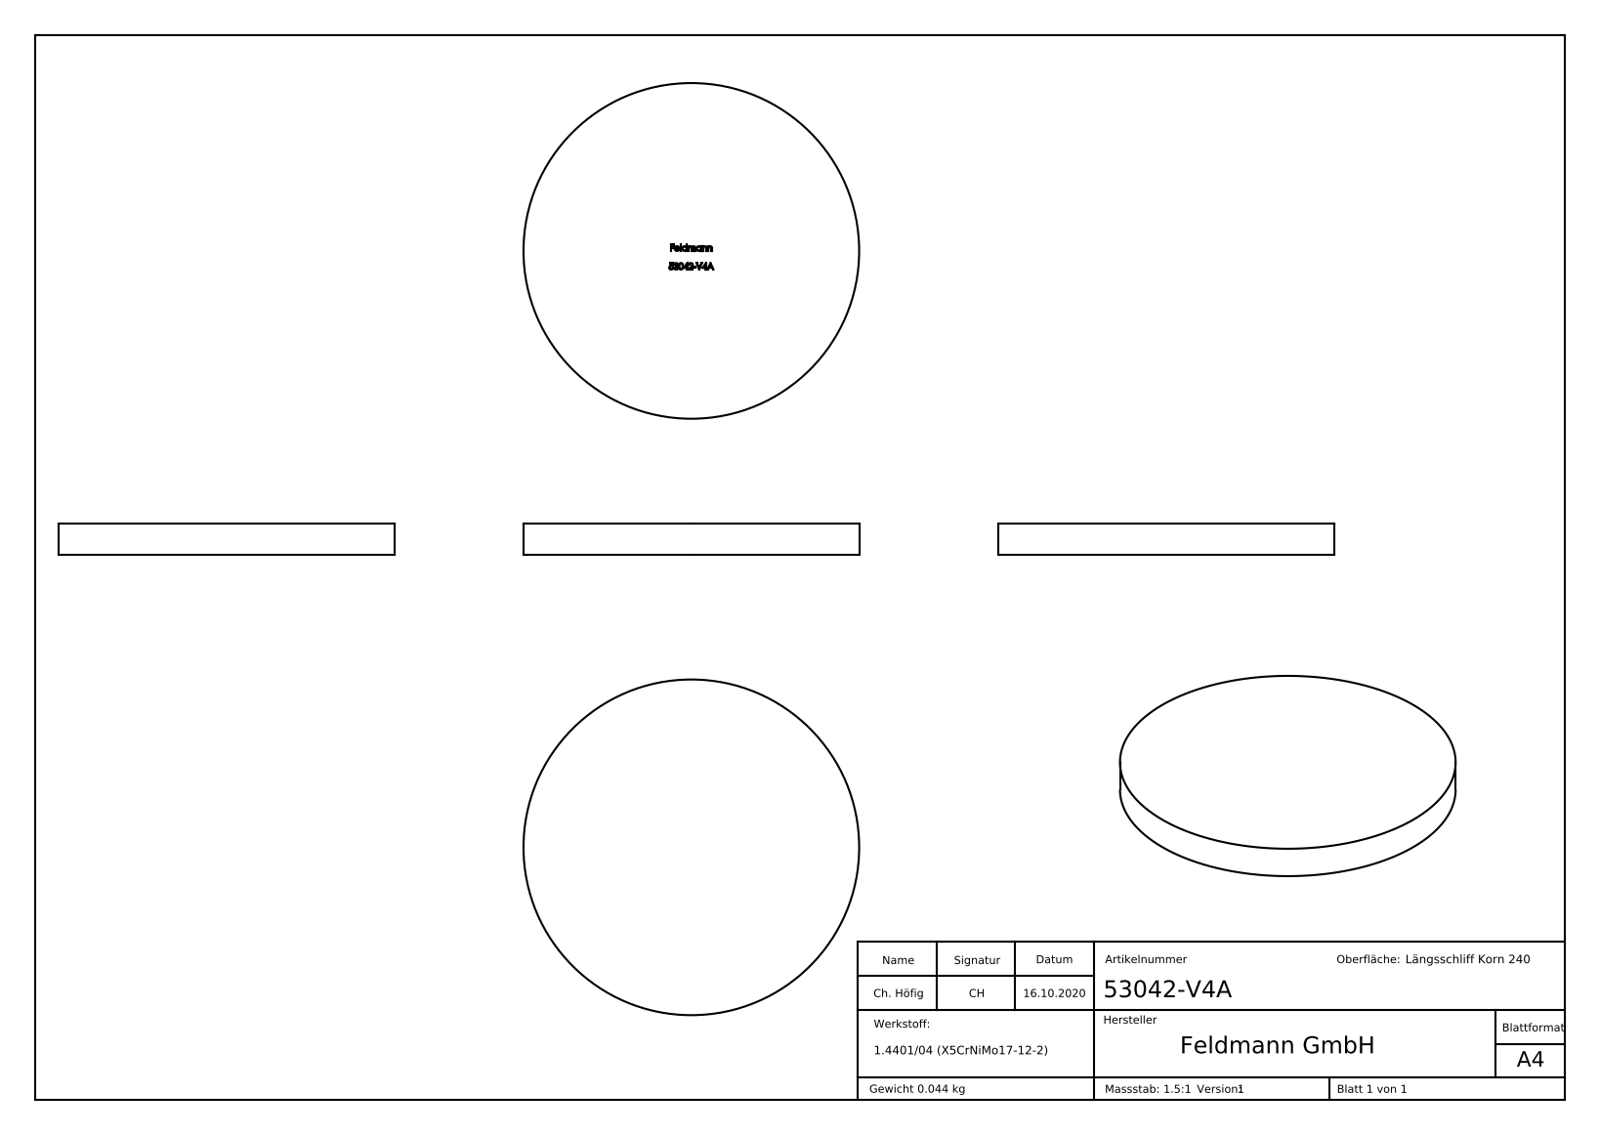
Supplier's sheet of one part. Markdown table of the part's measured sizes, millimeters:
| quantity | value |
| --- | --- |
| part name | 53042-V4A |
| STEP written by | SolidWorks 2018 (CONFIG_CONTROL_DESIGN) |
| units | millimeters |
| bodies | 1 solid, 230 faces (143 planar, 2 cylindrical, 85 other) |
| overall size | 42 × 42 × 4 |
| volume | 5 542 mm³ |
| surface area | 3 304 mm² |
| round bosses / shafts (diameter × count) | 42 × 1 |
| main face-to-face distances | 4, 3.9, 0.79, 0.99, 2, 1.78, 1.93, 0.83, 0.44, 2.77 |
